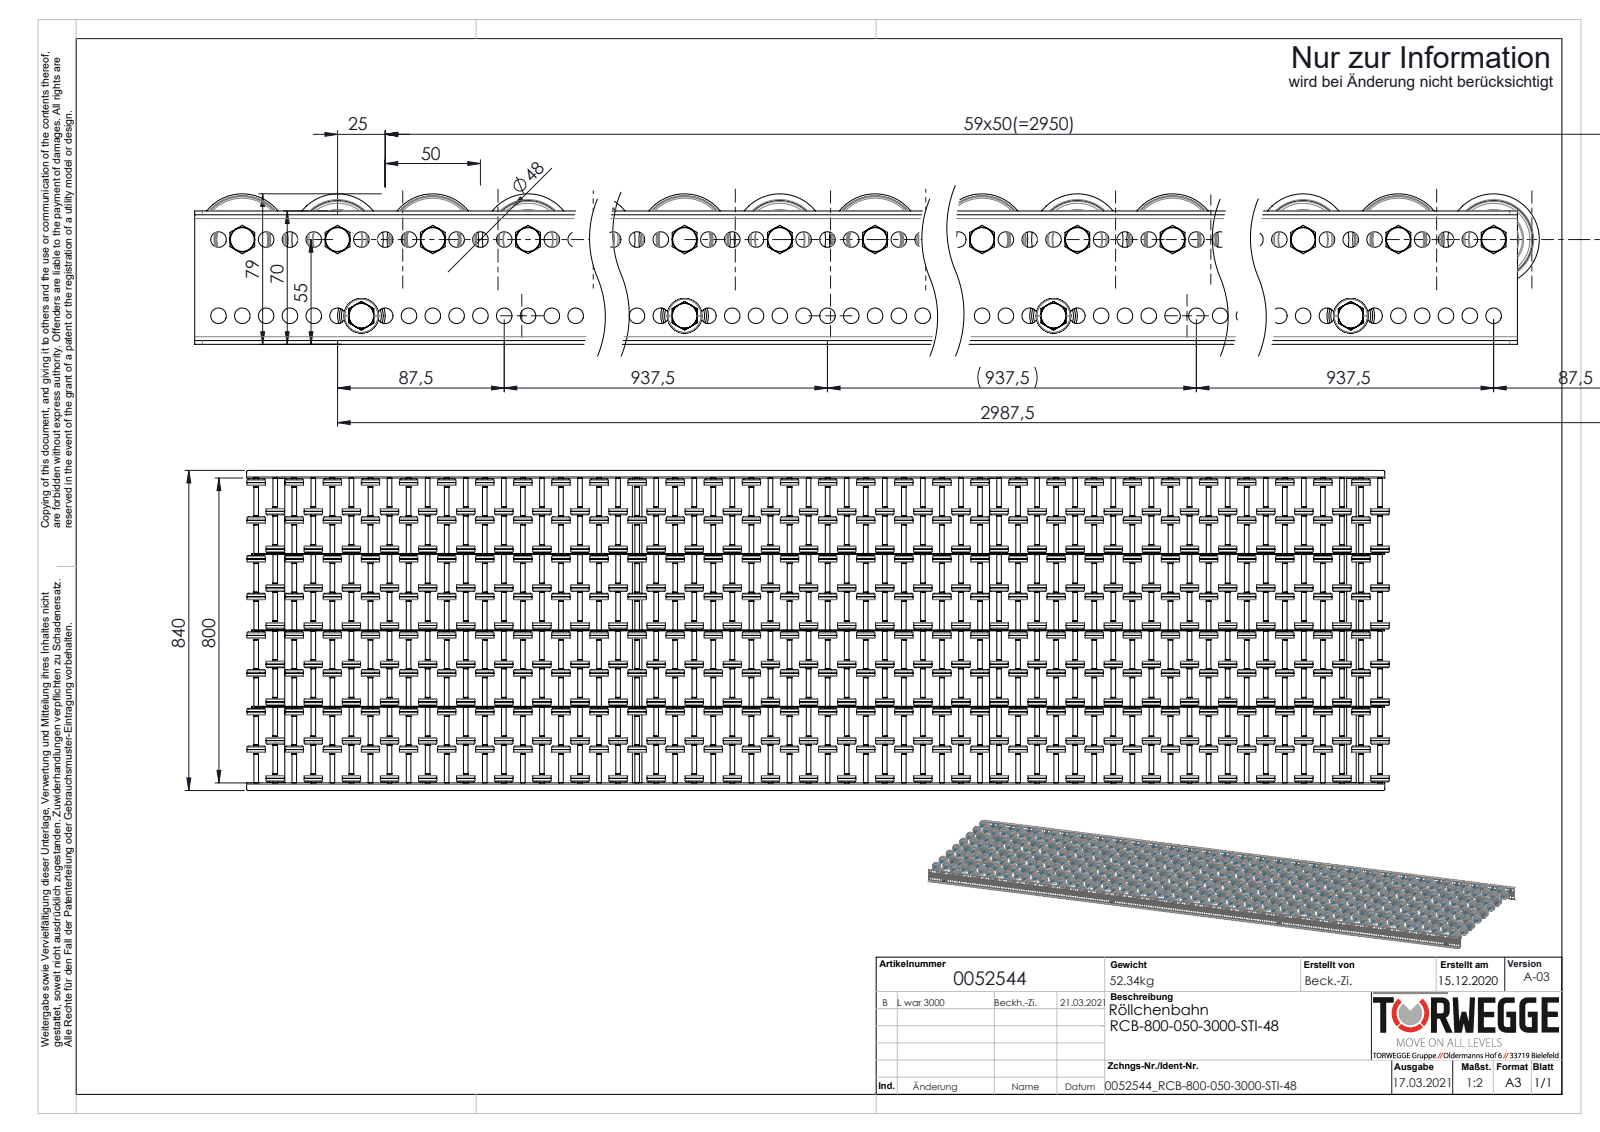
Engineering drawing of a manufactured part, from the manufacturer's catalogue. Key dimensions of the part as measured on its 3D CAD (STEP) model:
Part name (STEP PRODUCT): Röllchenachse-für-Konfiguration_EL800 Stahl; Traversen_KFG_L800; K0011528_2200-48-8; S100100_Längstraverse-42x2,5_S100104_Lngstraverse-RB-L3000 (+6 more)
STEP written by: SolidWorks 2020 (AUTOMOTIVE_DESIGN)
Units: millimetres
Bodies: 1645 solids, 48276 faces (9942 planar, 17726 cylindrical, 20608 other)
Overall size (bounding box): 2999 × 840 × 79
Volume: 16 630 000 mm³ · Surface area: 12 200 000 mm²
Round holes (diameter × count): ⌀8.2 ×476, ⌀8.5 ×119, ⌀6.65 ×60, ⌀8 ×60, ⌀9.65 ×60, ⌀15 ×60, ⌀41 ×60, ⌀6.8 ×4, ⌀21 ×4
Round bosses / shafts (diameter × count): ⌀48 ×60, ⌀13 ×60, ⌀12.5 ×60, ⌀12.4 ×60, ⌀12 ×60, ⌀11.5 ×60, ⌀25 ×4, ⌀8 ×4
Partial cylindrical surfaces — rounded edges, fillets, slot ends (radius × count): R4 ×8, R2 ×4, R5 ×4
Main face-to-face distances: 200.5, 401, 12, 2, 601.5, 89.5, 188.5, 212.5, 99, 111
Hole centre spacings: 12.5, 25, 37.5, 50, 62.5, 75, 87.5, 100
